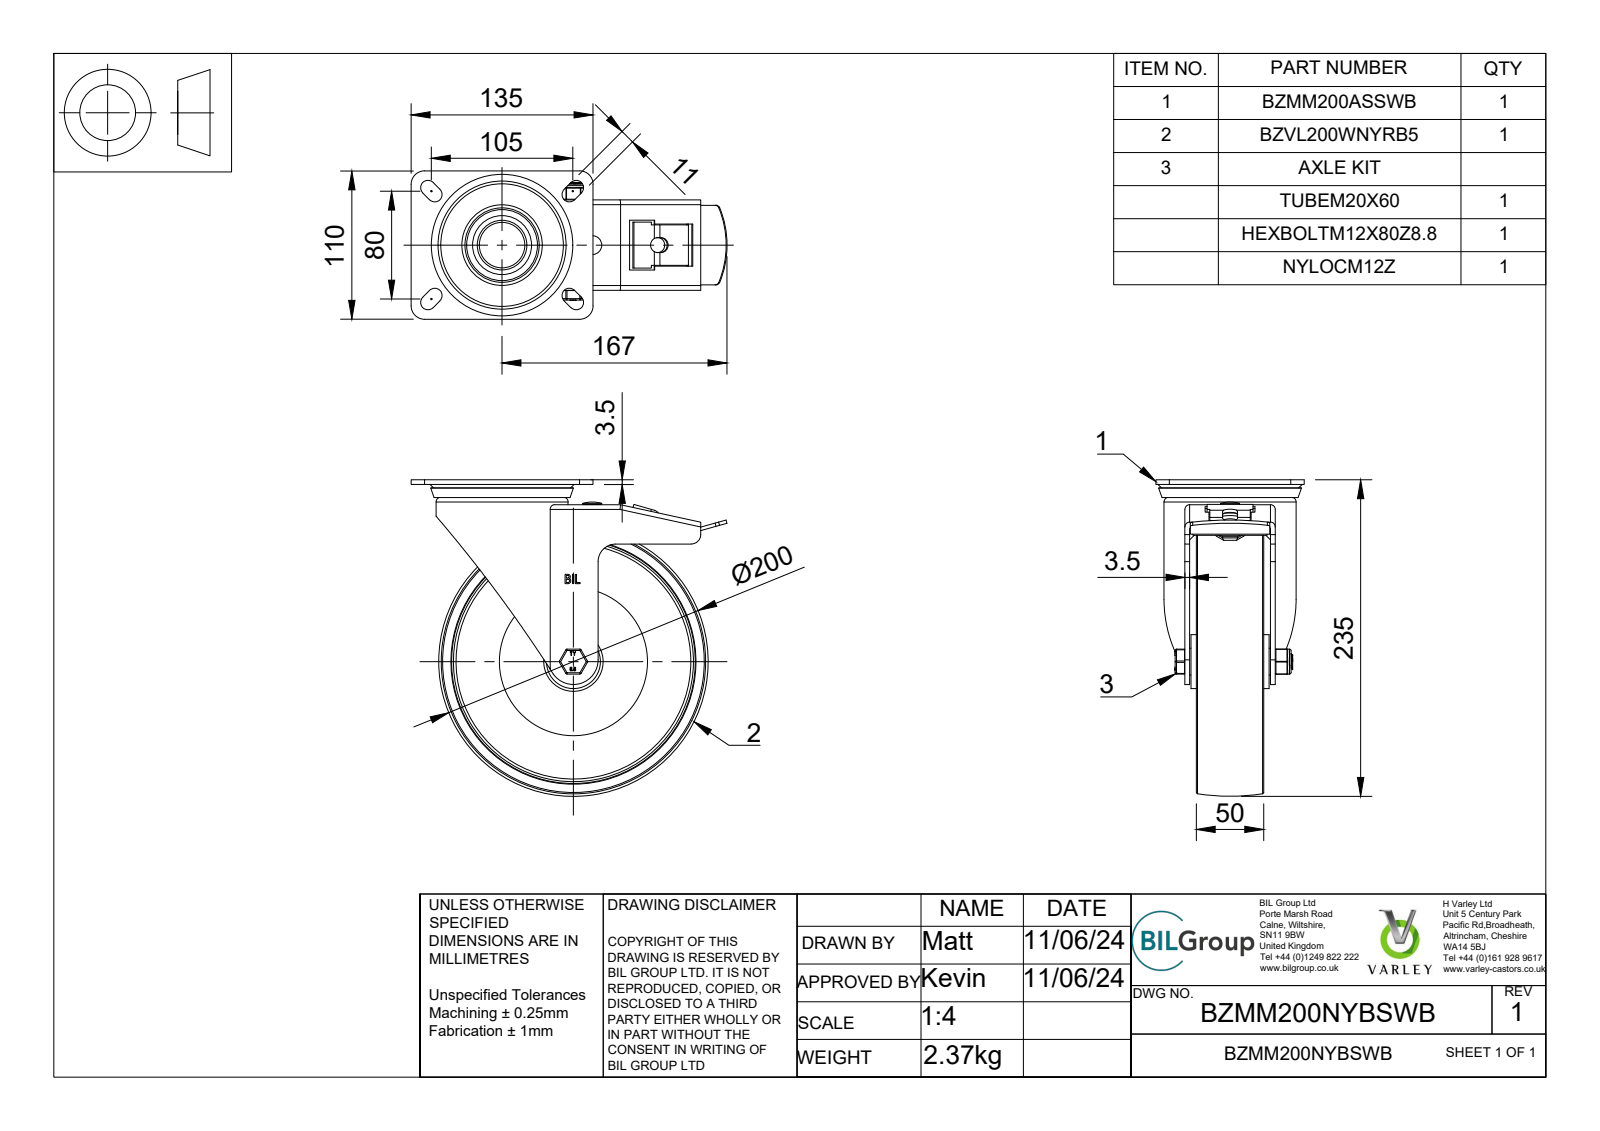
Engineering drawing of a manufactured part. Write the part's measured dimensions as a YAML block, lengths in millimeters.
part_name: "BZMM200NYBSWB v4; BZMM200ASSWB v1; ZINC PLATED, PRESSED STEEL TOP PLATE; ZINC PLATED, PRESSED STEEL TOP PLATE Geometry (+7 more)"
step_written_by: "Autodesk Translation Framework v13.14.0.145 (AUTOMOTIVE_DESIGN)"
units: millimeters
bodies: {solids: 63, faces: 638, planar: 311, cylindrical: 183, other: 144}
overall_size: [235, 234.5, 110]
volume: 828699
surface_area: 303816
round_holes:
  - {diameter: 8, count: 1}
  - {diameter: 11, count: 1}
  - {diameter: 12, count: 1}
  - {diameter: 12.2, count: 1}
  - {diameter: 12.5, count: 1}
  - {diameter: 14, count: 1}
  - {diameter: 20, count: 1}
  - {diameter: 20.2, count: 1}
  - {diameter: 33.75, count: 1}
  - {diameter: 61, count: 1}
  - {diameter: 91, count: 1}
round_bosses_or_shafts:
  - {diameter: 7.5, count: 8}
  - {diameter: 98, count: 1}
  - {diameter: 78, count: 1}
  - {diameter: 50, count: 1}
  - {diameter: 40, count: 1}
  - {diameter: 39.75, count: 1}
  - {diameter: 34, count: 1}
  - {diameter: 19.9, count: 1}
partial_cylinders:
  - {radius: 0.5, count: 18}
  - {radius: 1, count: 12}
  - {radius: 5.5, count: 10}
  - {radius: 1.75, count: 7}
  - {radius: 0.25, count: 6}
  - {radius: 2.5, count: 6}
  - {radius: 3.5, count: 4}
  - {radius: 10, count: 4}
face_to_face_distances: [3.5, 9.5, 4, 5, 9, 34.75, 28.75, 38.25, 13, 63.5]
hole_center_spacings: [67]
